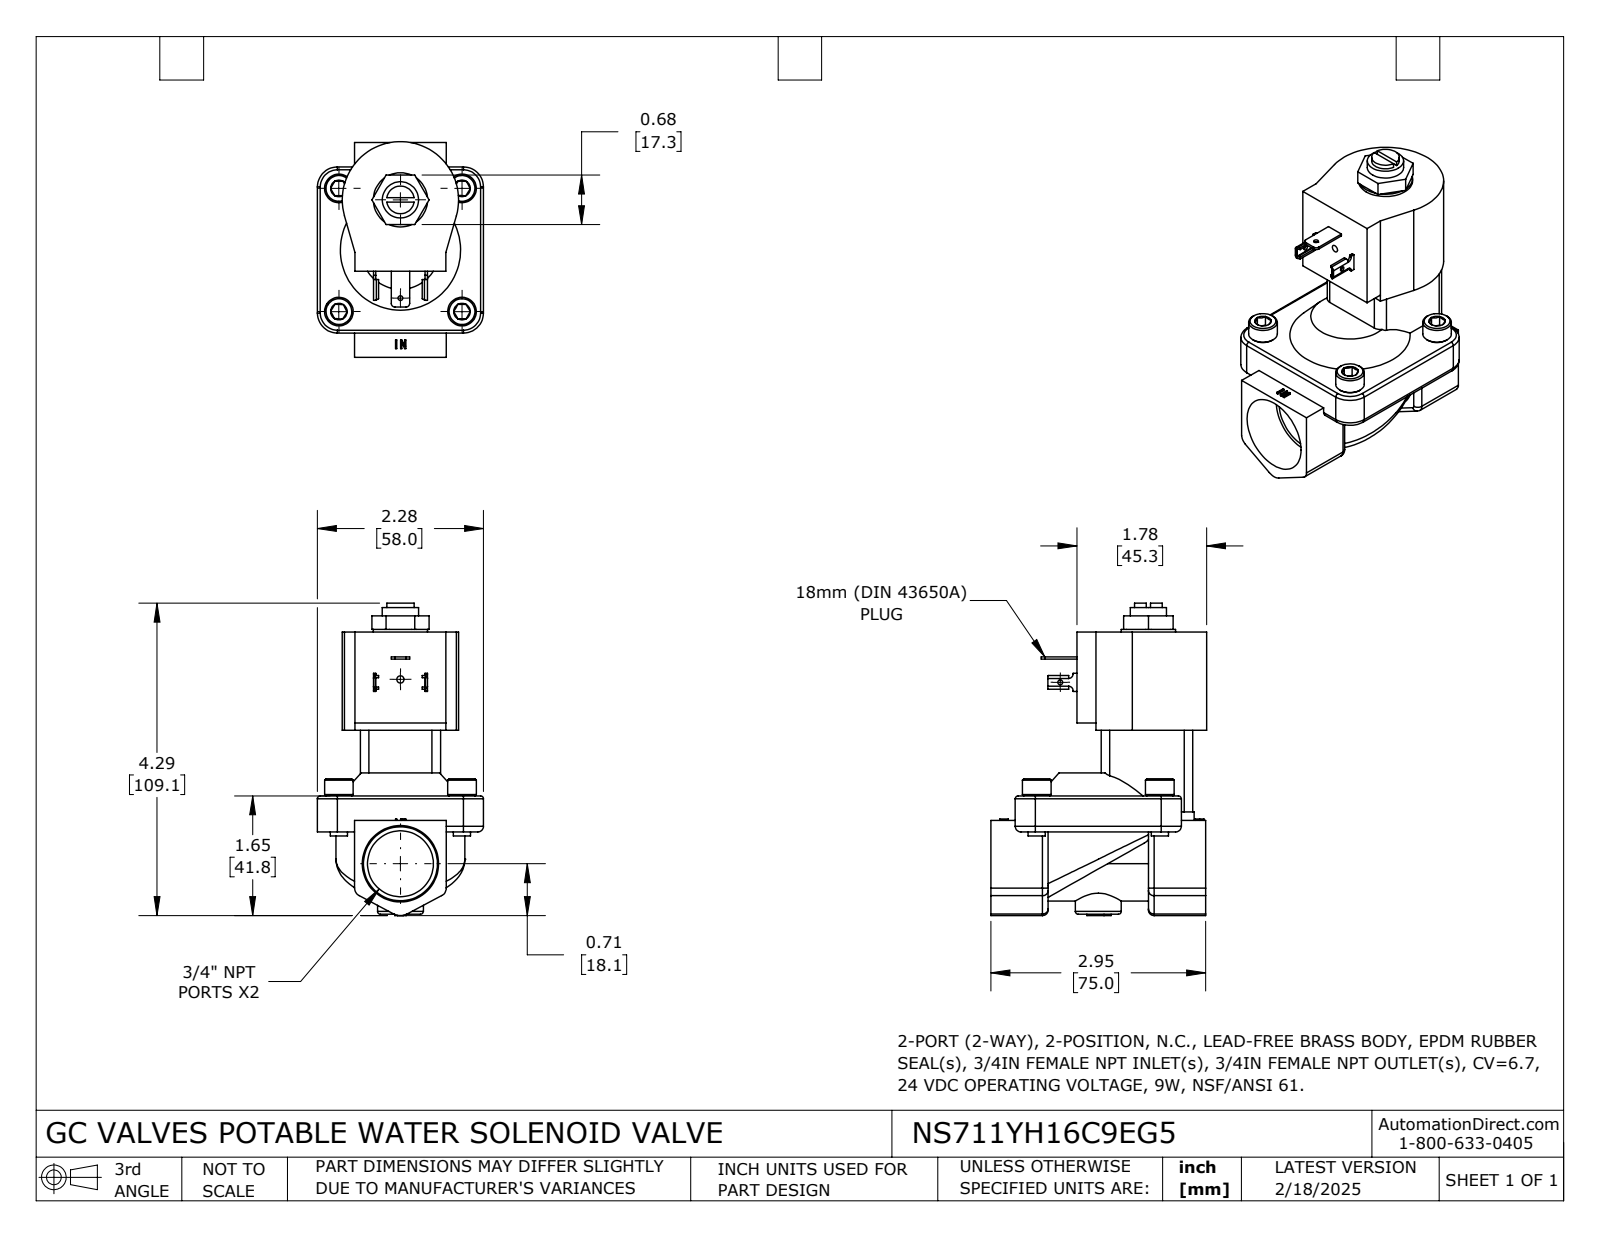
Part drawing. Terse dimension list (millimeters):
name: NS711YH16C9EG5
written by: SolidWorks 2024 (CONFIG_CONTROL_DESIGN)
unit: mm
bodies: 1 solid, 366 faces (189 planar, 92 cylindrical, 85 other)
size: 109.07 × 75.32 × 58
volume: 158 585 mm³; area: 32 388 mm²
holes: 1× ⌀1.68, 1× ⌀1.7, 1× ⌀2.53, 1× ⌀23.01, 1× ⌀30.48
bosses: 4× ⌀10, 4× ⌀6, 1× ⌀18.95, 1× ⌀16, 1× ⌀12.67, 1× ⌀9.65
rounds: 11× R2, 6× R3, 4× R0.15, 4× R1, 4× R1.04, 4× R7, 2× R1.27, 2× R1.52
face distances: 30, 2, 57.19, 32, 22.9, 34.29, 43, 15, 13, 45
hole spacings: 34.29, 64.36
